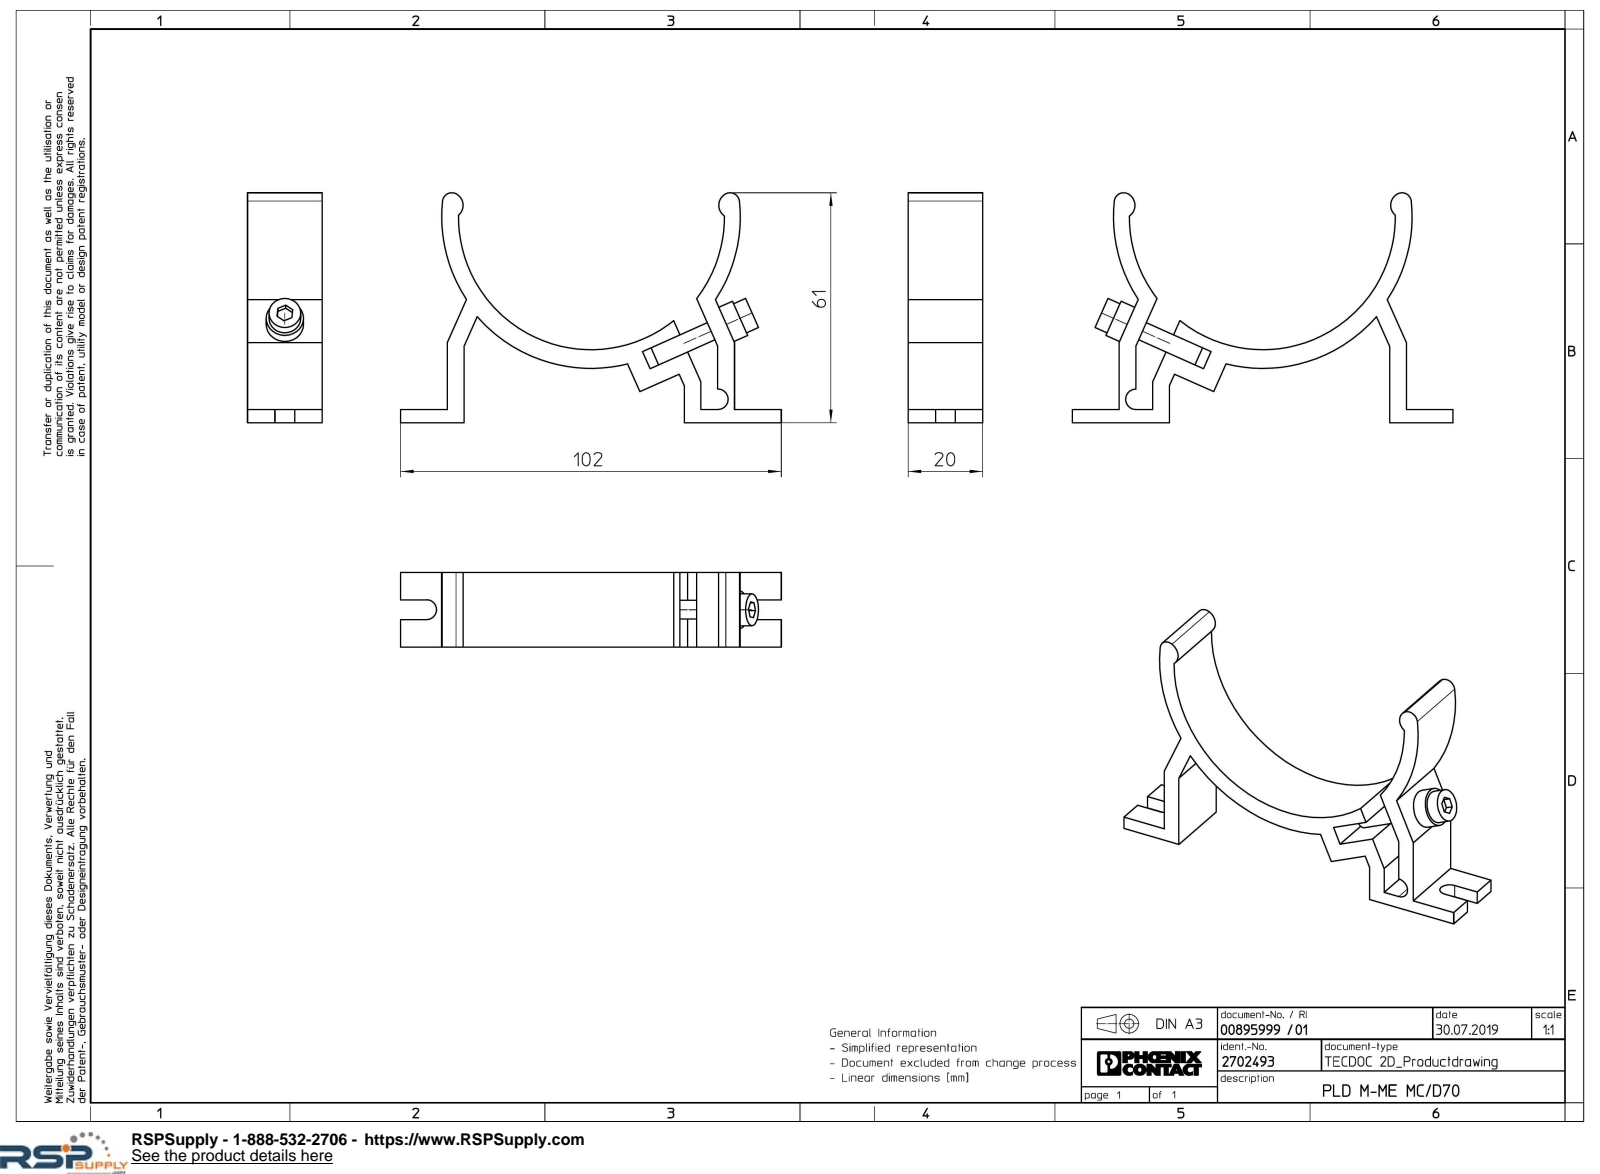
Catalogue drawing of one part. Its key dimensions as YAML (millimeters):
part_name: "PLD_M_ME_MC_D70-select"
step_written_by: "Creo Elements/Direct Modeling 20.1A 29-Sep-2018 (C) Parametric Technology GmbH (AUTOMOTIVE_DESIGN)"
units: millimeters
bodies: {solids: 1, faces: 61, planar: 43, cylindrical: 18, other: 0}
overall_size: [102, 61.46, 20]
volume: 22323
surface_area: 12840
round_bosses_or_shafts:
  - {diameter: 10, count: 1}
  - {diameter: 8.5, count: 1}
  - {diameter: 5, count: 1}
partial_cylinders:
  - {radius: 2.5, count: 2}
  - {radius: 2.65, count: 2}
  - {radius: 3.5, count: 2}
  - {radius: 2.75, count: 1}
  - {radius: 35.5, count: 1}
  - {radius: 35.75, count: 1}
  - {radius: 40, count: 1}
  - {radius: 40.5, count: 1}
face_to_face_distances: [4.5, 20, 72.5, 3.5, 68, 77, 63.5, 9, 8.01, 12.51]
